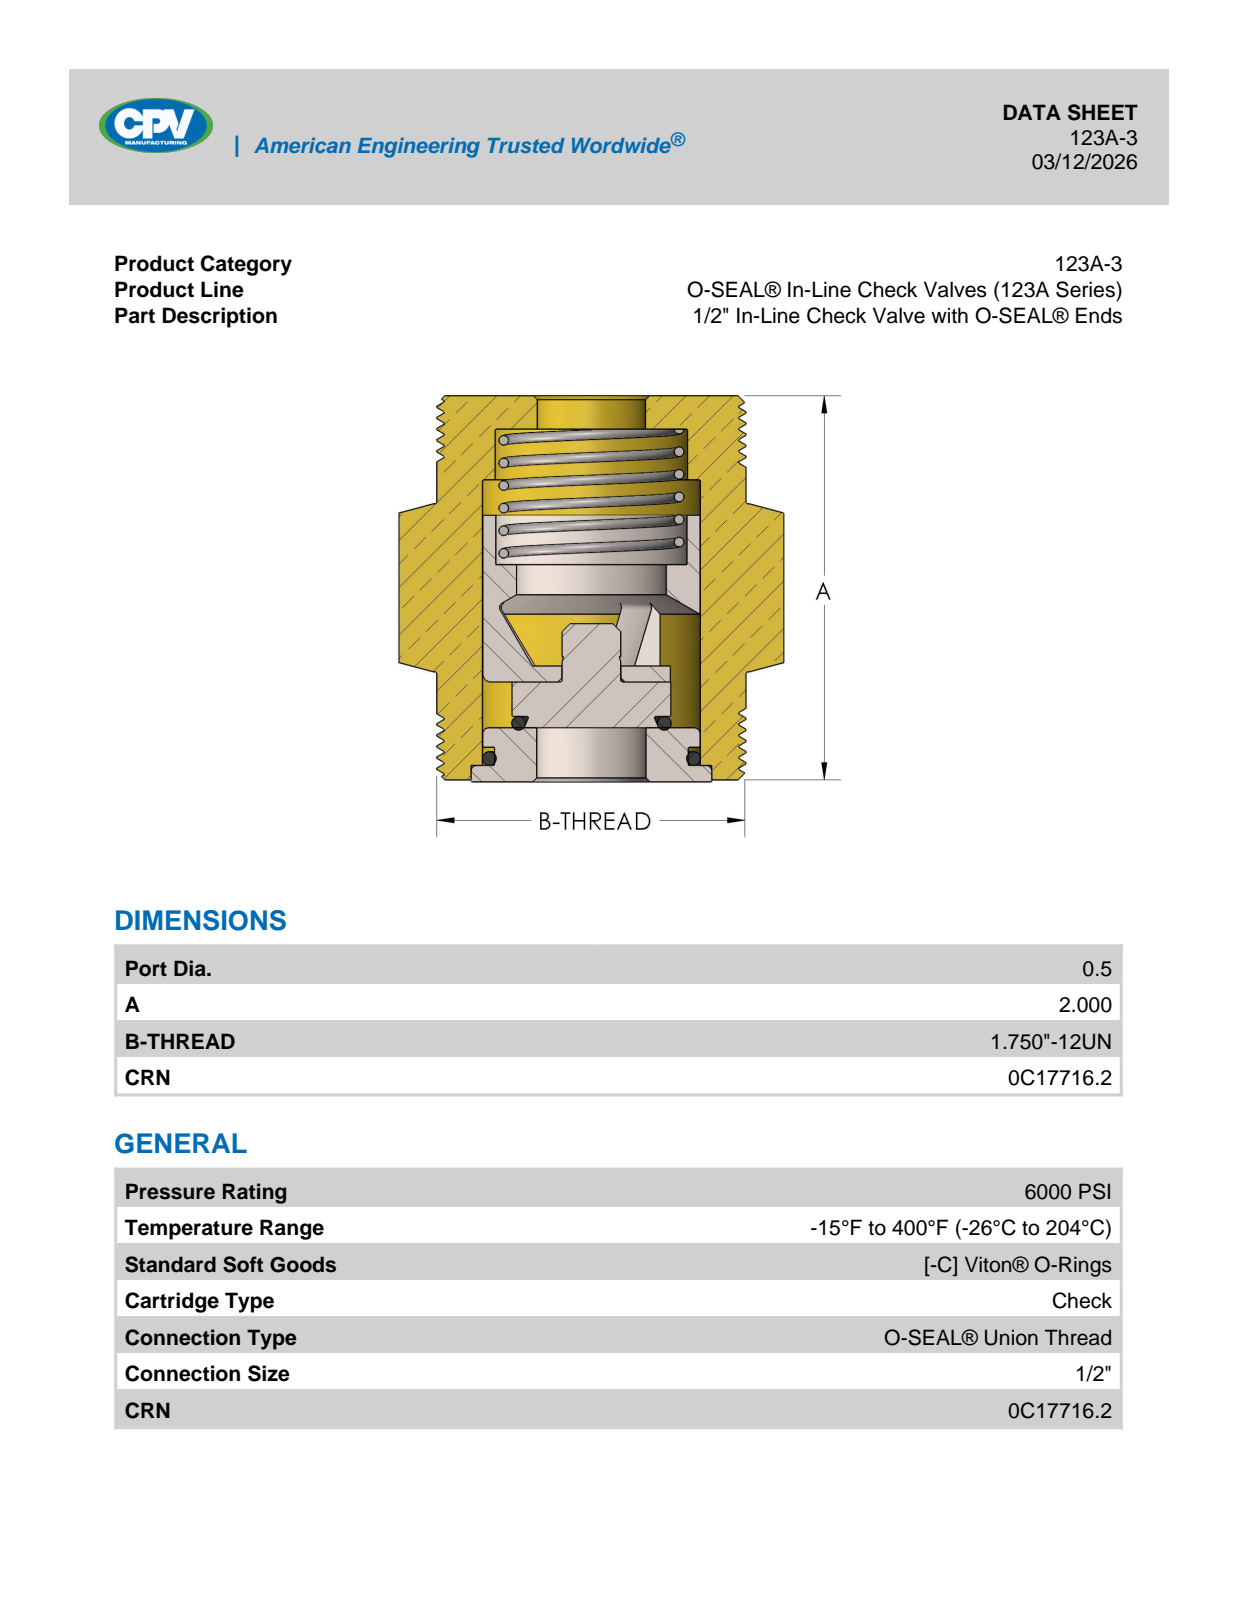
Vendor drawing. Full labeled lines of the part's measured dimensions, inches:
Part name (STEP PRODUCT): 123A-3
STEP written by: SolidWorks 2018 (AUTOMOTIVE_DESIGN)
Units: inches
Bodies: 1 solid, 73 faces (15 planar, 30 cylindrical, 28 other)
Overall size (bounding box): 2.171 × 2.015 × 1.88
Volume: 4.965 in³ · Surface area: 21.3 in²
Round holes (diameter × count): ⌀0.5 ×1, ⌀0.505 ×1
Round bosses / shafts (diameter × count): ⌀1.745 ×1, ⌀1.365 ×1
Main face-to-face distances: 1.88, 2.015, 0.015, 2, 1.325, 1.31, 0.69, 0.705, 0.69, 0.62
